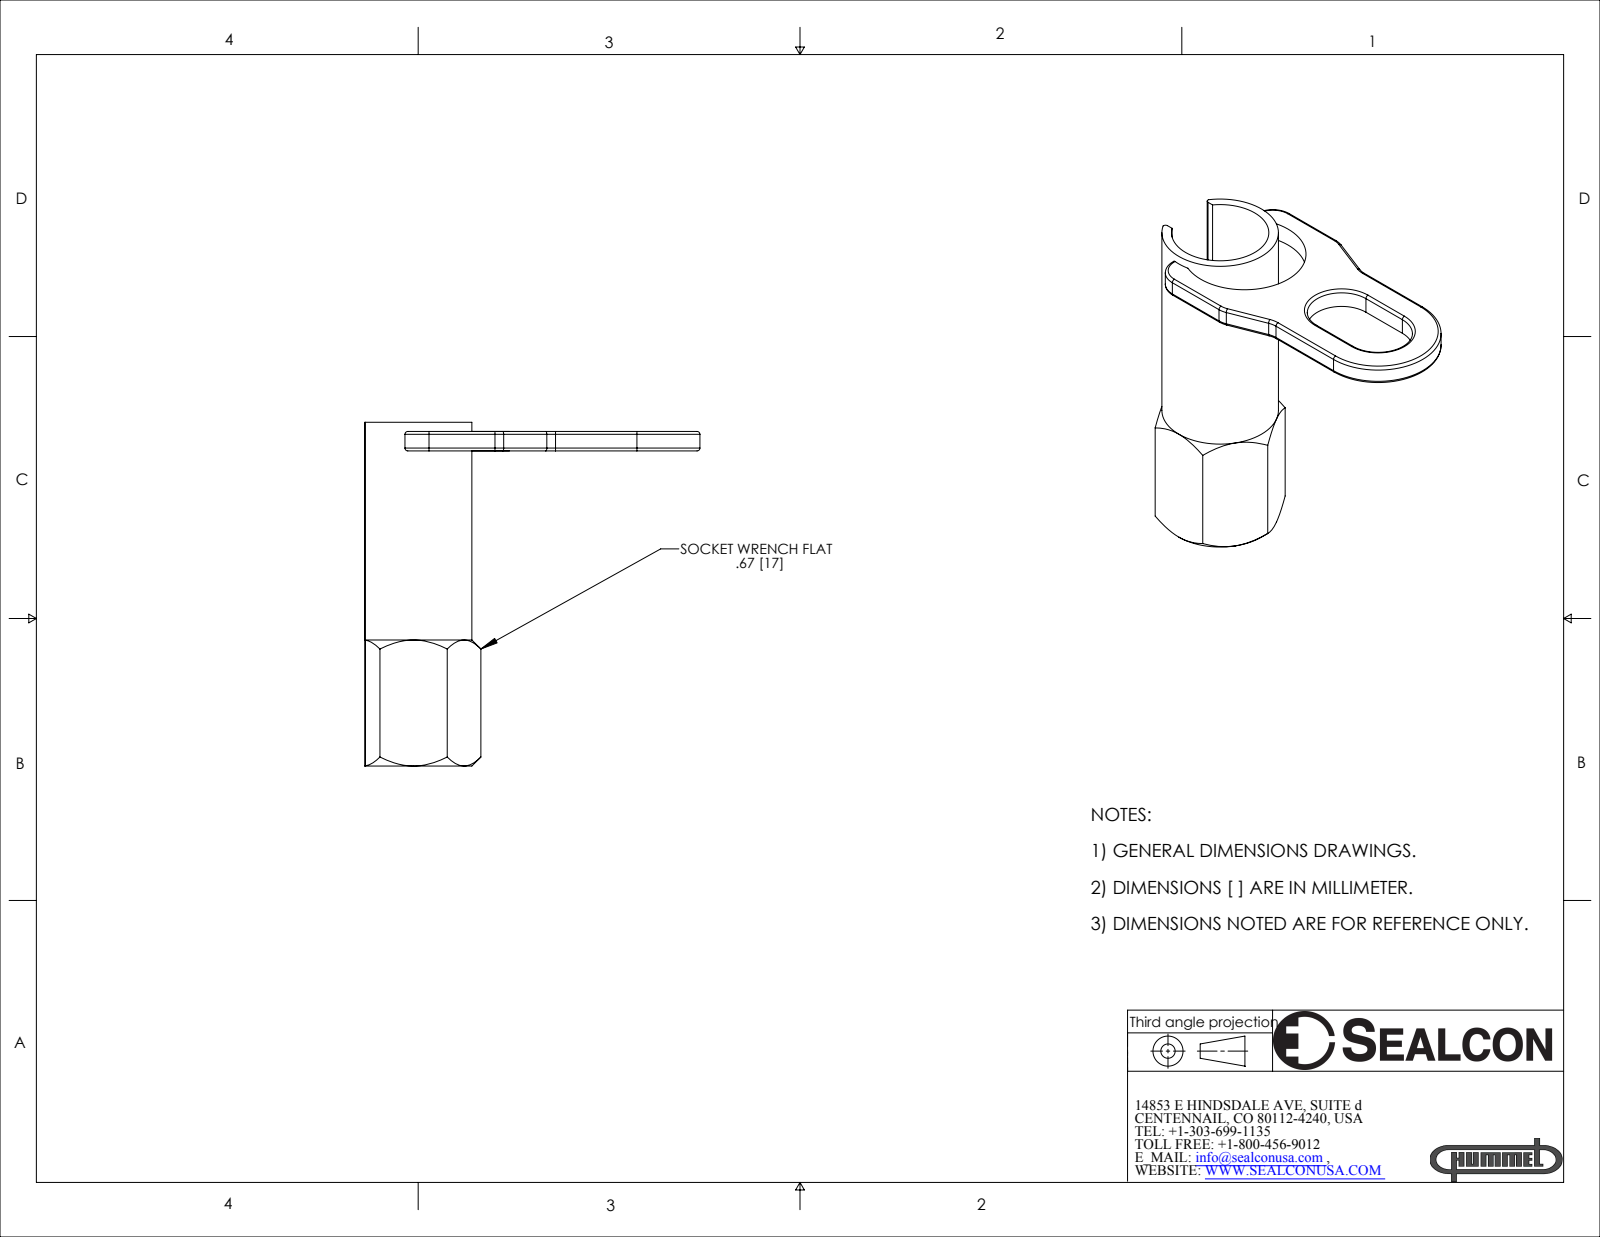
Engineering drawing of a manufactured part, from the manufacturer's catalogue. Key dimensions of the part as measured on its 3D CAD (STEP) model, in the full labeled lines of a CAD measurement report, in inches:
Part name (STEP PRODUCT): S-1700-WR
STEP written by: SolidWorks 2007 (CONFIG_CONTROL_DESIGN)
Units: inches
Bodies: 1 solid, 96 faces (31 planar, 37 cylindrical, 28 other)
Overall size (bounding box): 2.362 × 2.303 × 1.142
Volume: 0.442 in³ · Surface area: 12.86 in²
Round holes (diameter × count): ⌀0.669 ×1
Round bosses / shafts (diameter × count): ⌀0.801 ×1
Partial cylindrical surfaces — rounded edges, fillets, slot ends (radius × count): R0.02 ×21, R0.165 ×6, R0.236 ×2, R0.423 ×1, R0.433 ×1
Main face-to-face distances: 0.066, 0.735, 0.134, 0.802, 0.669, 0.138, 0.204, 0.598, 0.531, 0.197
